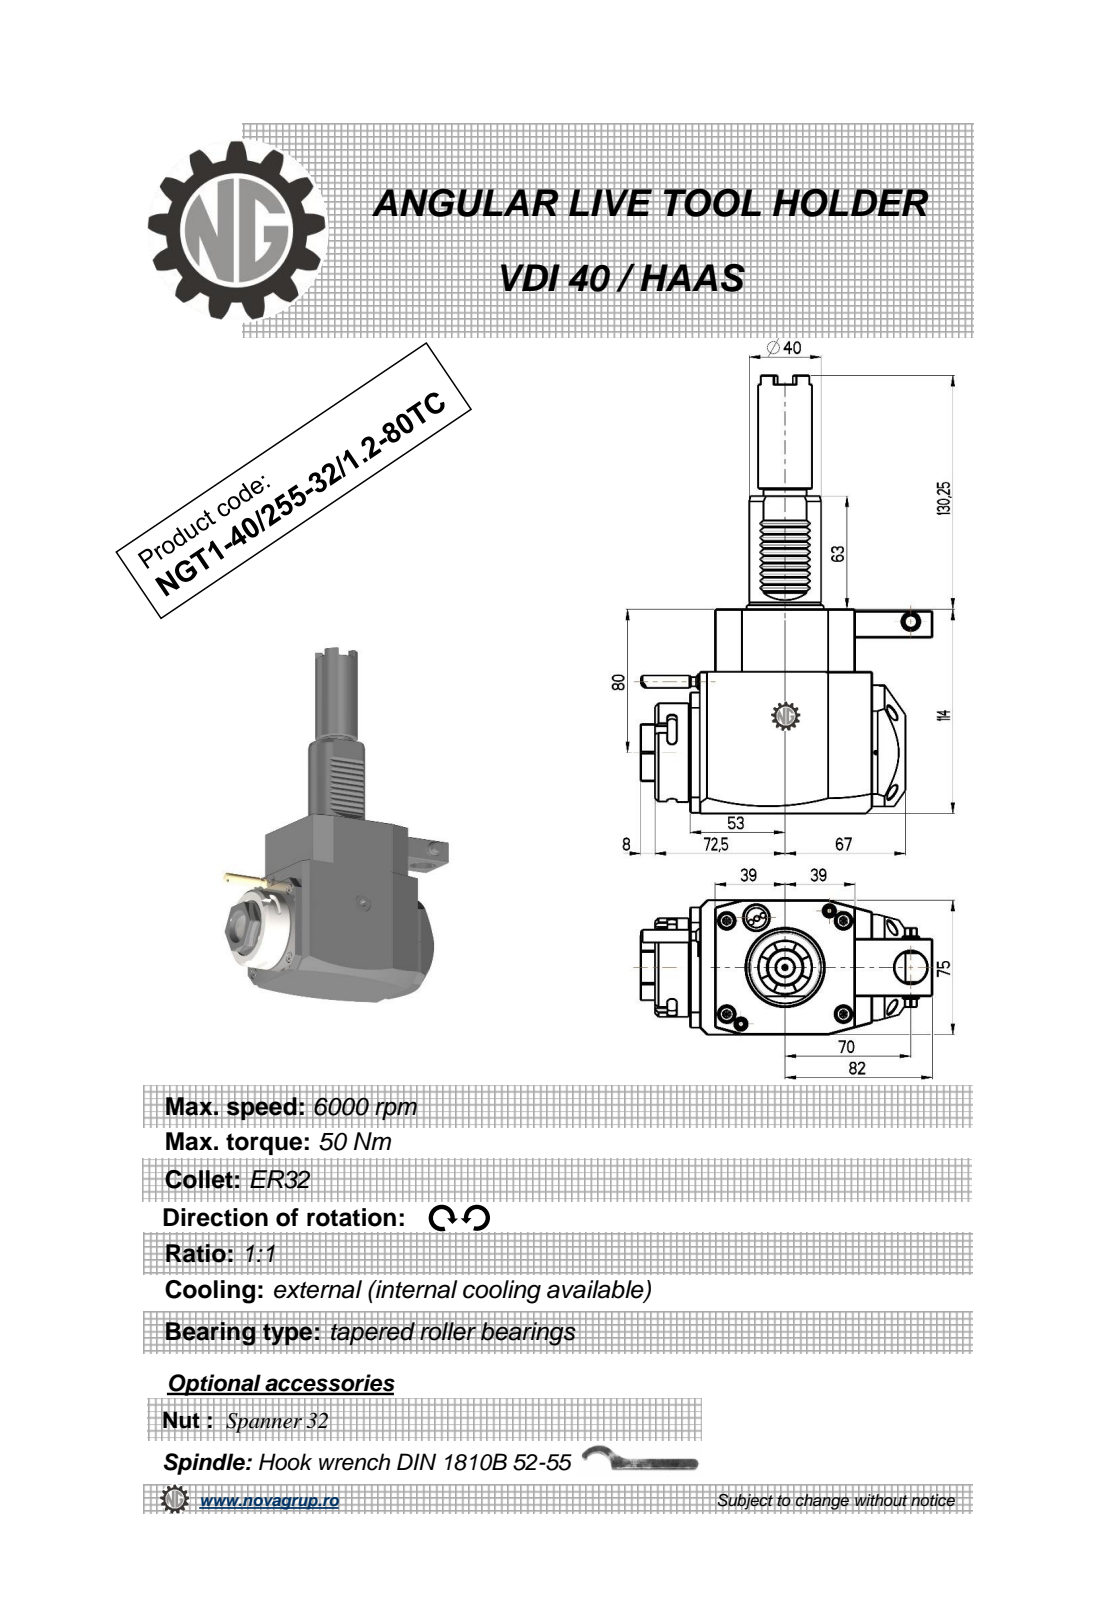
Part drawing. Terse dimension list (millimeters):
name: NGT1_40_255_32_1_2_80TC
written by: PRO/ENGINEER BY PARAMETRIC TECHNOLOGY CORPORATION, 2010280 (CONFIG_CONTROL_DESIGN)
unit: mm
bodies: 1 solid, 379 faces (219 planar, 76 cylindrical, 84 other)
size: 244.25 × 162.5 × 75
volume: 1 009 000 mm³; area: 80 730 mm²
holes: 1× ⌀2.5, 1× ⌀3, 1× ⌀9.5, 1× ⌀18, 1× ⌀20, 1× ⌀23
bosses: 2× ⌀8.96, 1× ⌀55, 1× ⌀48, 1× ⌀40, 1× ⌀30, 1× ⌀24, 1× ⌀10, 1× ⌀7
rounds: 10× R0.3, 6× R2.5, 2× R180, 1× R0.5, 1× R3.85, 1× R4.25, 1× R24.5, 1× R37.5
face distances: 75, 114, 14, 33.5, 79, 92, 78, 21.5, 98, 19.5
hole spacings: 37.35, 43.2, 70, 72.5
